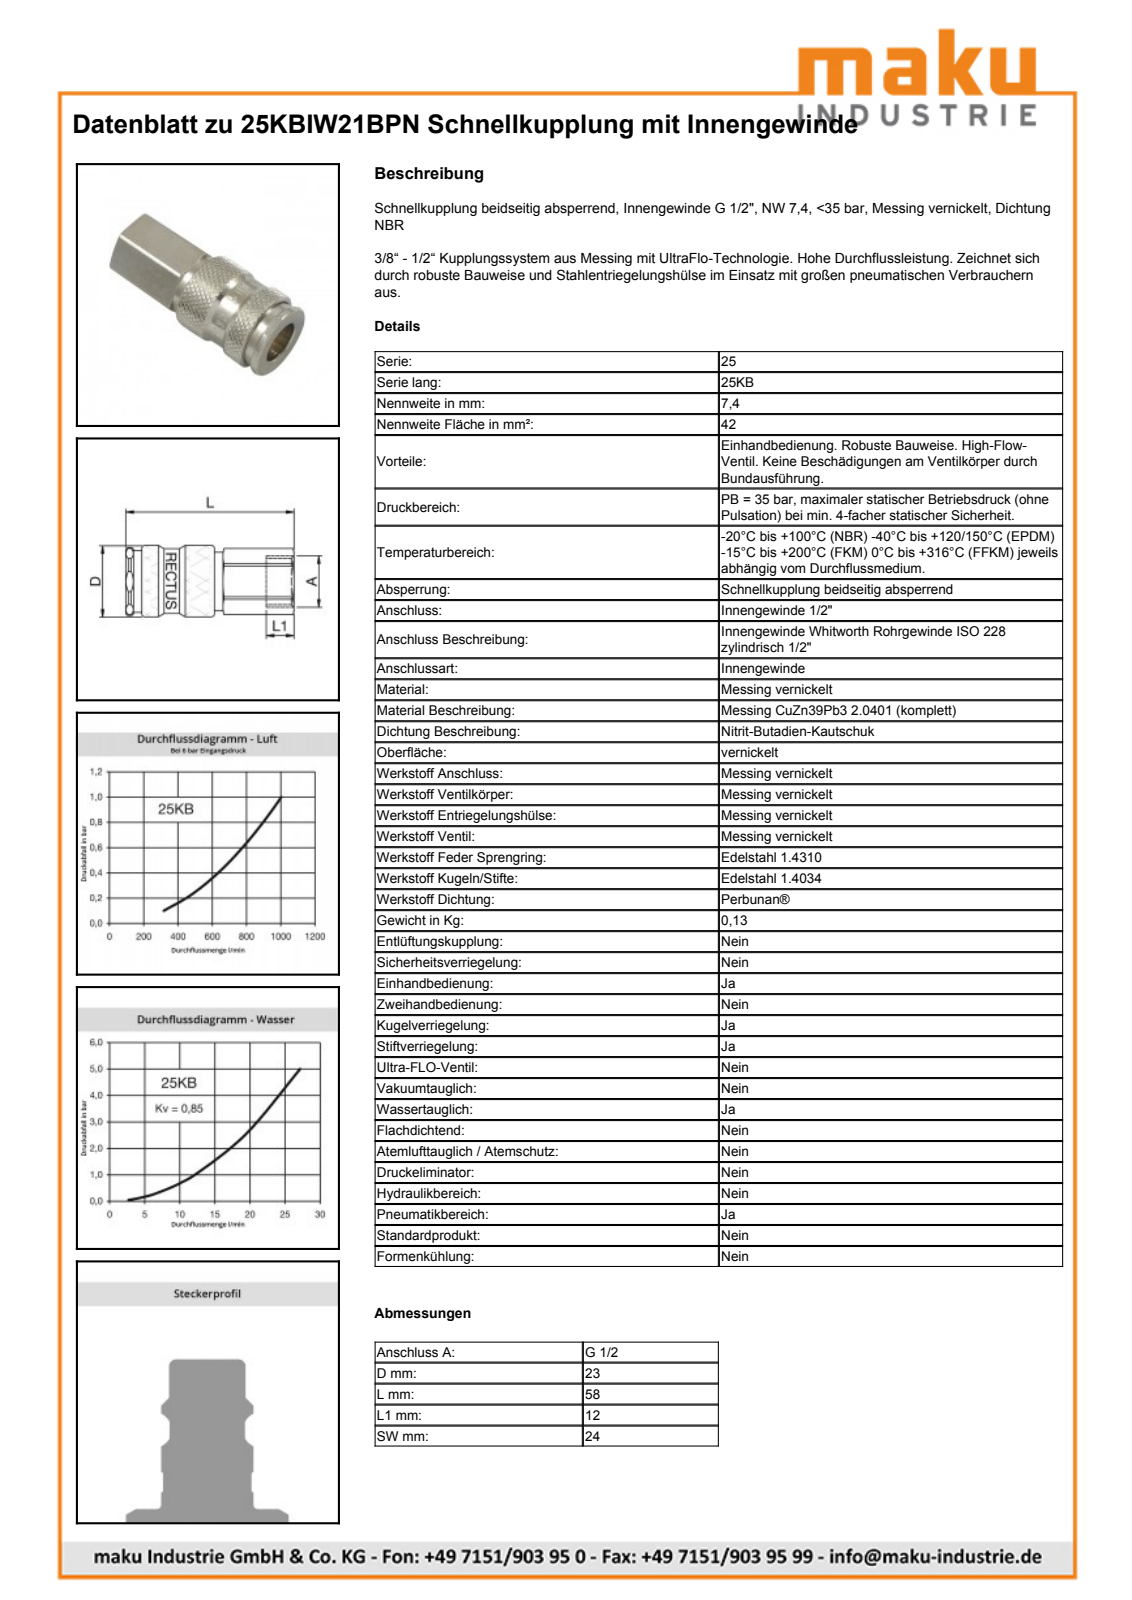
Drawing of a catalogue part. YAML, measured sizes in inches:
part_name: "D110568"
step_written_by: "Autodesk Inventor 2013 (AUTOMOTIVE_DESIGN)"
units: inches
bodies: {solids: 2, faces: 737, planar: 251, cylindrical: 82, other: 404}
overall_size: [2.264, 1.049, 1.028]
volume: 1.232
surface_area: 14.6
round_holes:
  - {diameter: 0.63, count: 1}
  - {diameter: 0.679, count: 1}
  - {diameter: 0.733, count: 1}
  - {diameter: 0.762, count: 1}
  - {diameter: 0.789, count: 1}
round_bosses_or_shafts:
  - {diameter: 0.911, count: 1}
  - {diameter: 0.827, count: 1}
  - {diameter: 0.787, count: 1}
  - {diameter: 0.746, count: 1}
  - {diameter: 0.607, count: 1}
partial_cylinders:
  - {radius: 0.311, count: 1}
  - {radius: 0.409, count: 1}
  - {radius: 0.433, count: 1}
  - {radius: 0.533, count: 1}
face_to_face_distances: [0.945, 1.791, 1.238, 0.553, 0.827, 2.264, 1.026, 0.472, 0.965, 0.274]
